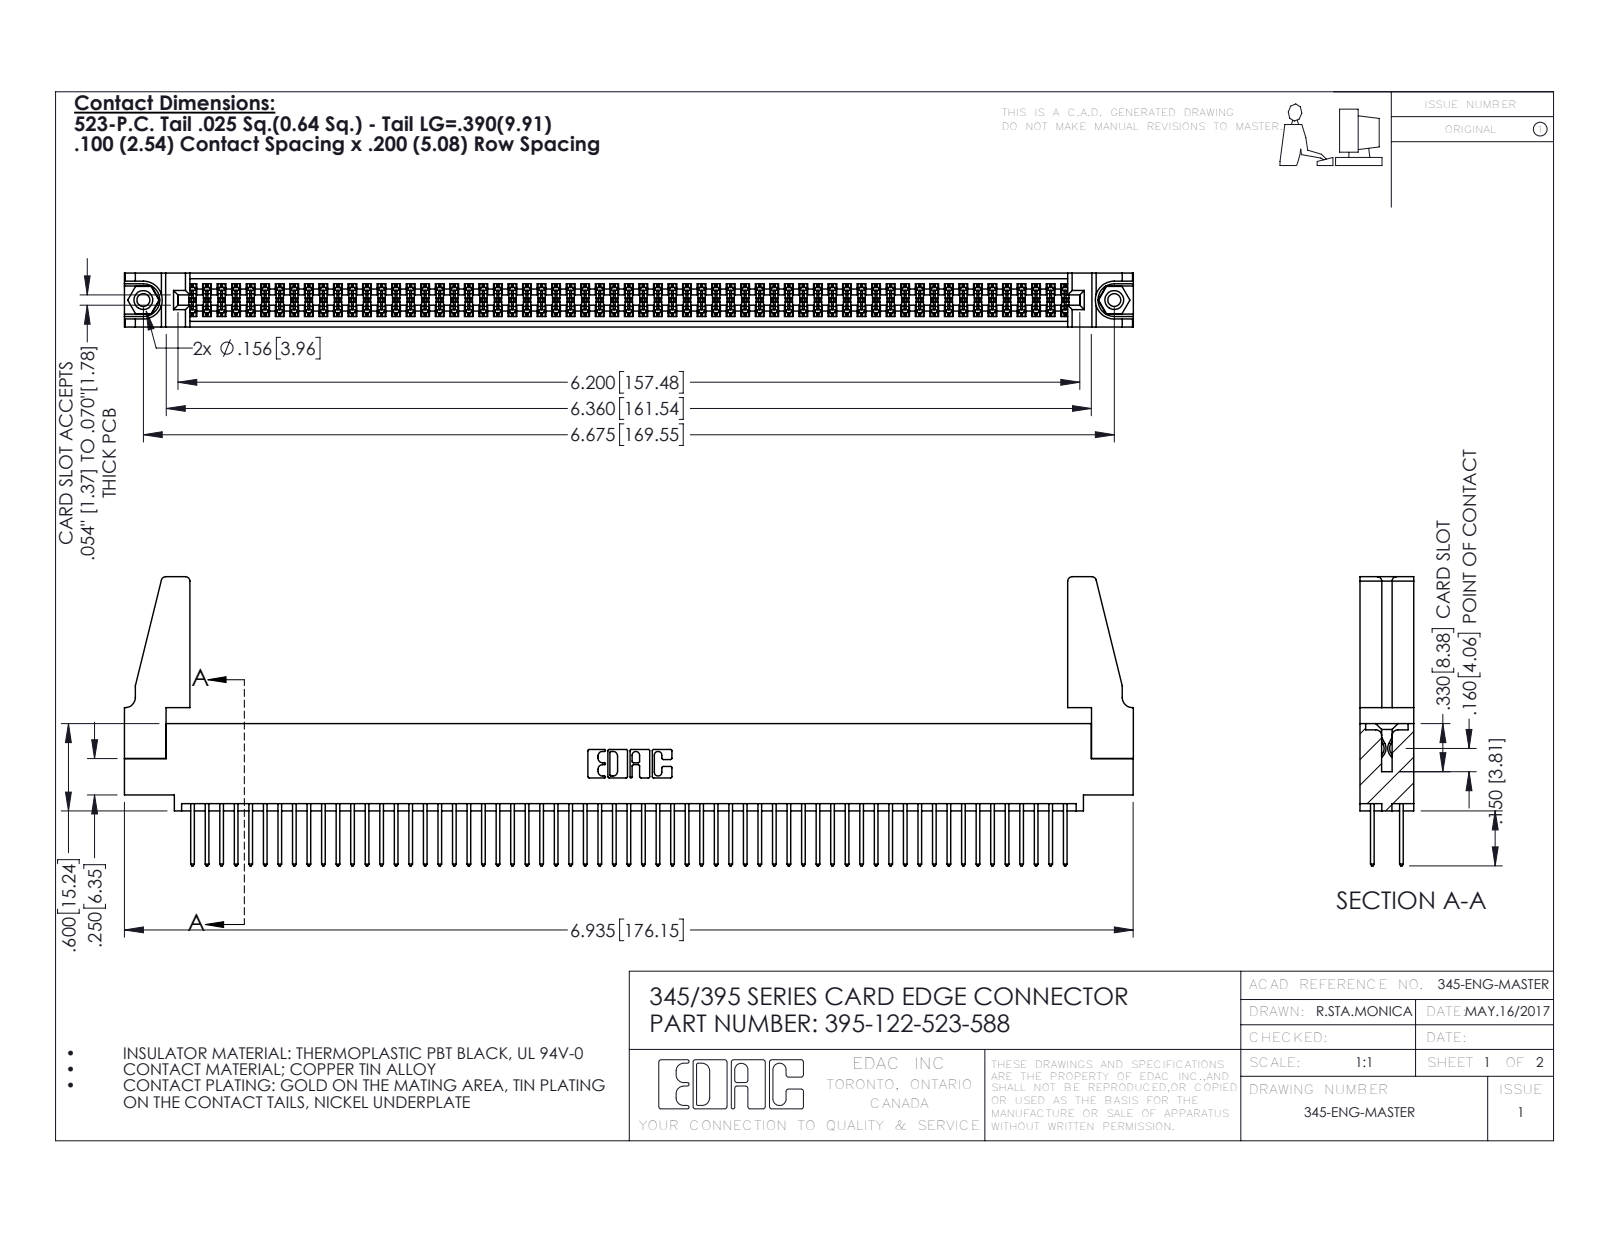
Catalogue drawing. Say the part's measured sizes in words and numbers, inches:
The part is named "345-250-001_345-250-001-102; 345-220-078_345-220-088; 345 Part_0.110 Offset - 0.156 Dia-TH; 395-122-523-588 (+1 more)". Its 3-D file was written by "SolidWorks 2016 (CONFIG_CONTROL_DESIGN)". It is 127 solids with 6354 faces: 4182 planar, 2156 cylindrical and 16 other. Overall it measures 6.936 by 1.987 by 0.37 inches. Its volume is 1.264 cubic inches and its surface area 47.31 square inches. Round holes: 2 of diameter 0.089, 2 of diameter 0.125, 2 of diameter 0.156, 1 of diameter 0.064. Round bosses or shafts: 2 of diameter 0.155. Partial cylindrical surfaces (rounded edges, fillets, slot ends): 183 of radius 0.006, 122 of radius 0.01, 22 of radius 0.01, 8 of radius 0.03, 6 of radius 0.007, 6 of radius 0.031, 3 of radius 0.026, 2 of radius 0.014. The main face-to-face distances are 0.072, 0.298, 0.2, 0.098, 0.272, 0.025, 0.37, 0.225, 0.175, 0.149. The hole center spacings are 0.27, 6.439, 6.675.
